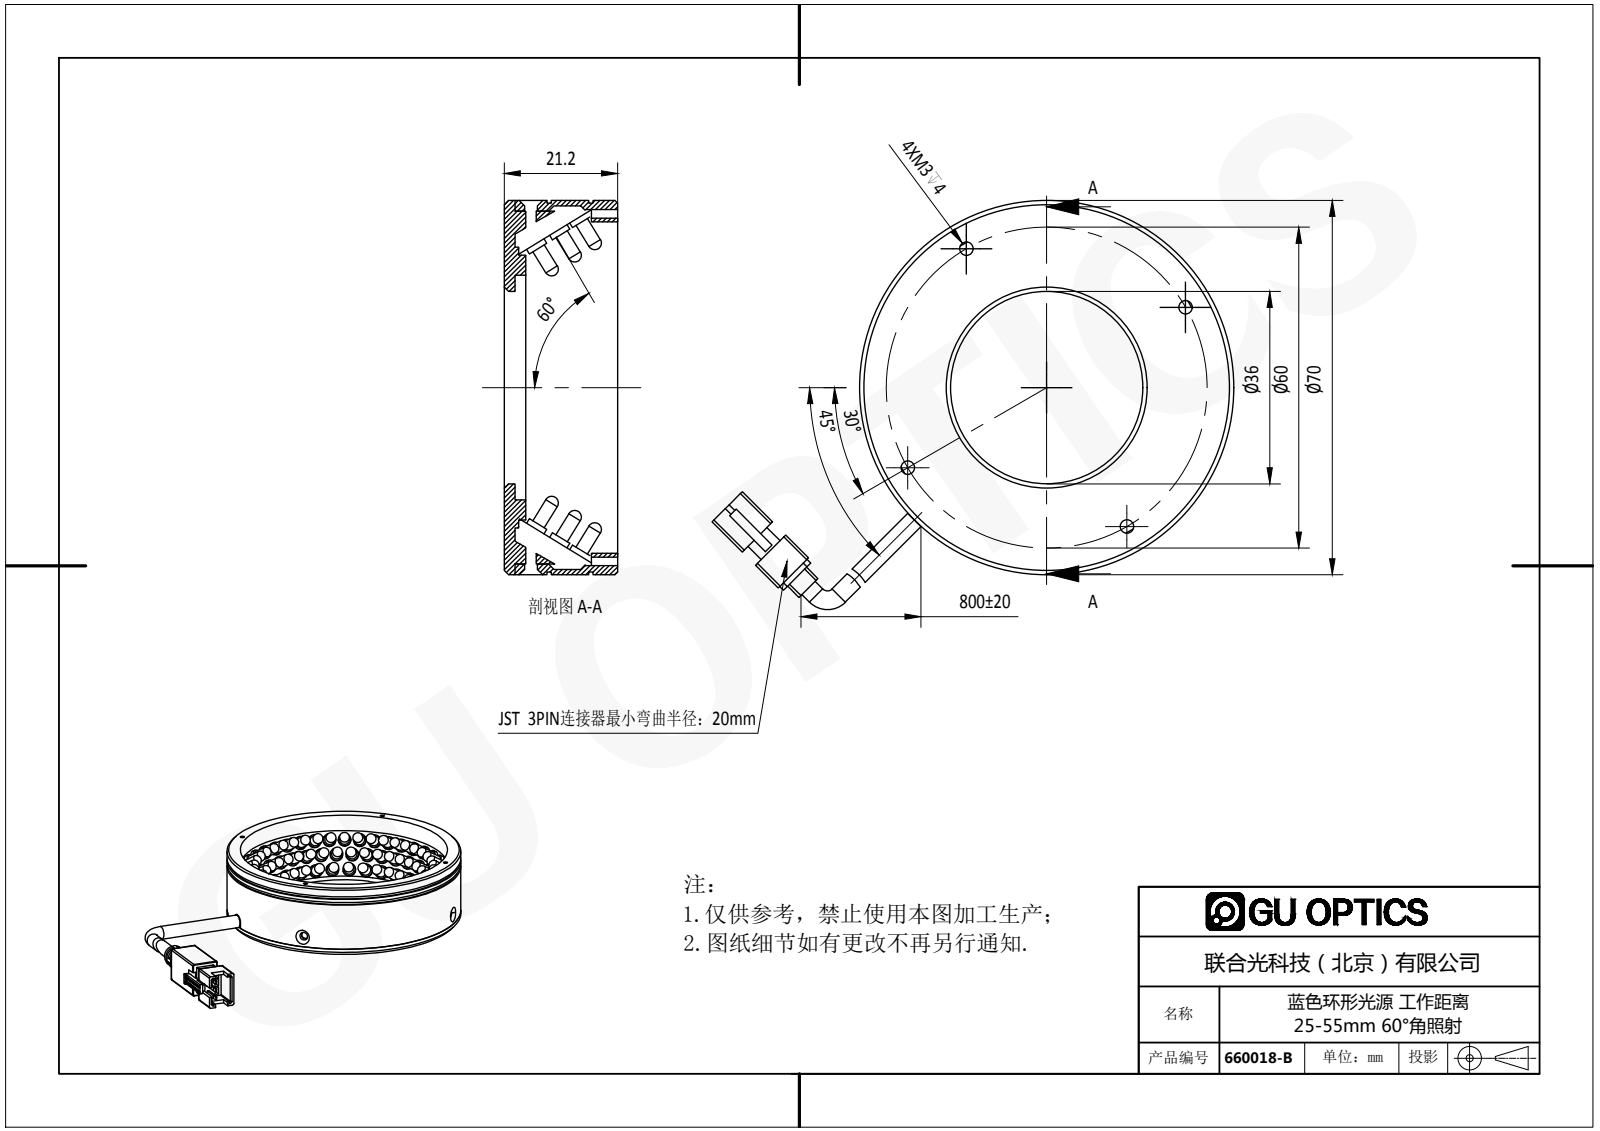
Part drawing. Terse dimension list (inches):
name: 660018-B
written by: SolidWorks 2016 (AUTOMOTIVE_DESIGN)
unit: in
bodies: 118 solids, 2275 faces (1503 planar, 596 cylindrical, 176 other)
size: 4.83 × 3.181 × 0.892
volume: 1.665 in³; area: 58.26 in²
holes: 4× ⌀0.049, 4× ⌀0.098, 3× ⌀0.15, 2× ⌀0.079, 2× ⌀0.094, 1× ⌀1.417, 1× ⌀1.654, 1× ⌀2.441, 1× ⌀2.598, 1× ⌀2.677
bosses: 112× ⌀0.15, 112× ⌀0.118, 1× ⌀2.756, 1× ⌀2.717, 1× ⌀2.067, 1× ⌀1.949, 1× ⌀0.138
rounds: 15× R0.004, 13× R0.008, 12× R0.016, 1× R0.012, 1× R0.027, 1× R0.055, 1× R0.065, 1× R0.177
face distances: 0.079, 0.039, 0.835, 0.756, 0.02, 0.106, 0.028, 0.728, 0.059, 0.535
hole spacings: 0.644, 1.181, 1.233, 1.28, 1.67, 1.809, 2.131, 2.377
